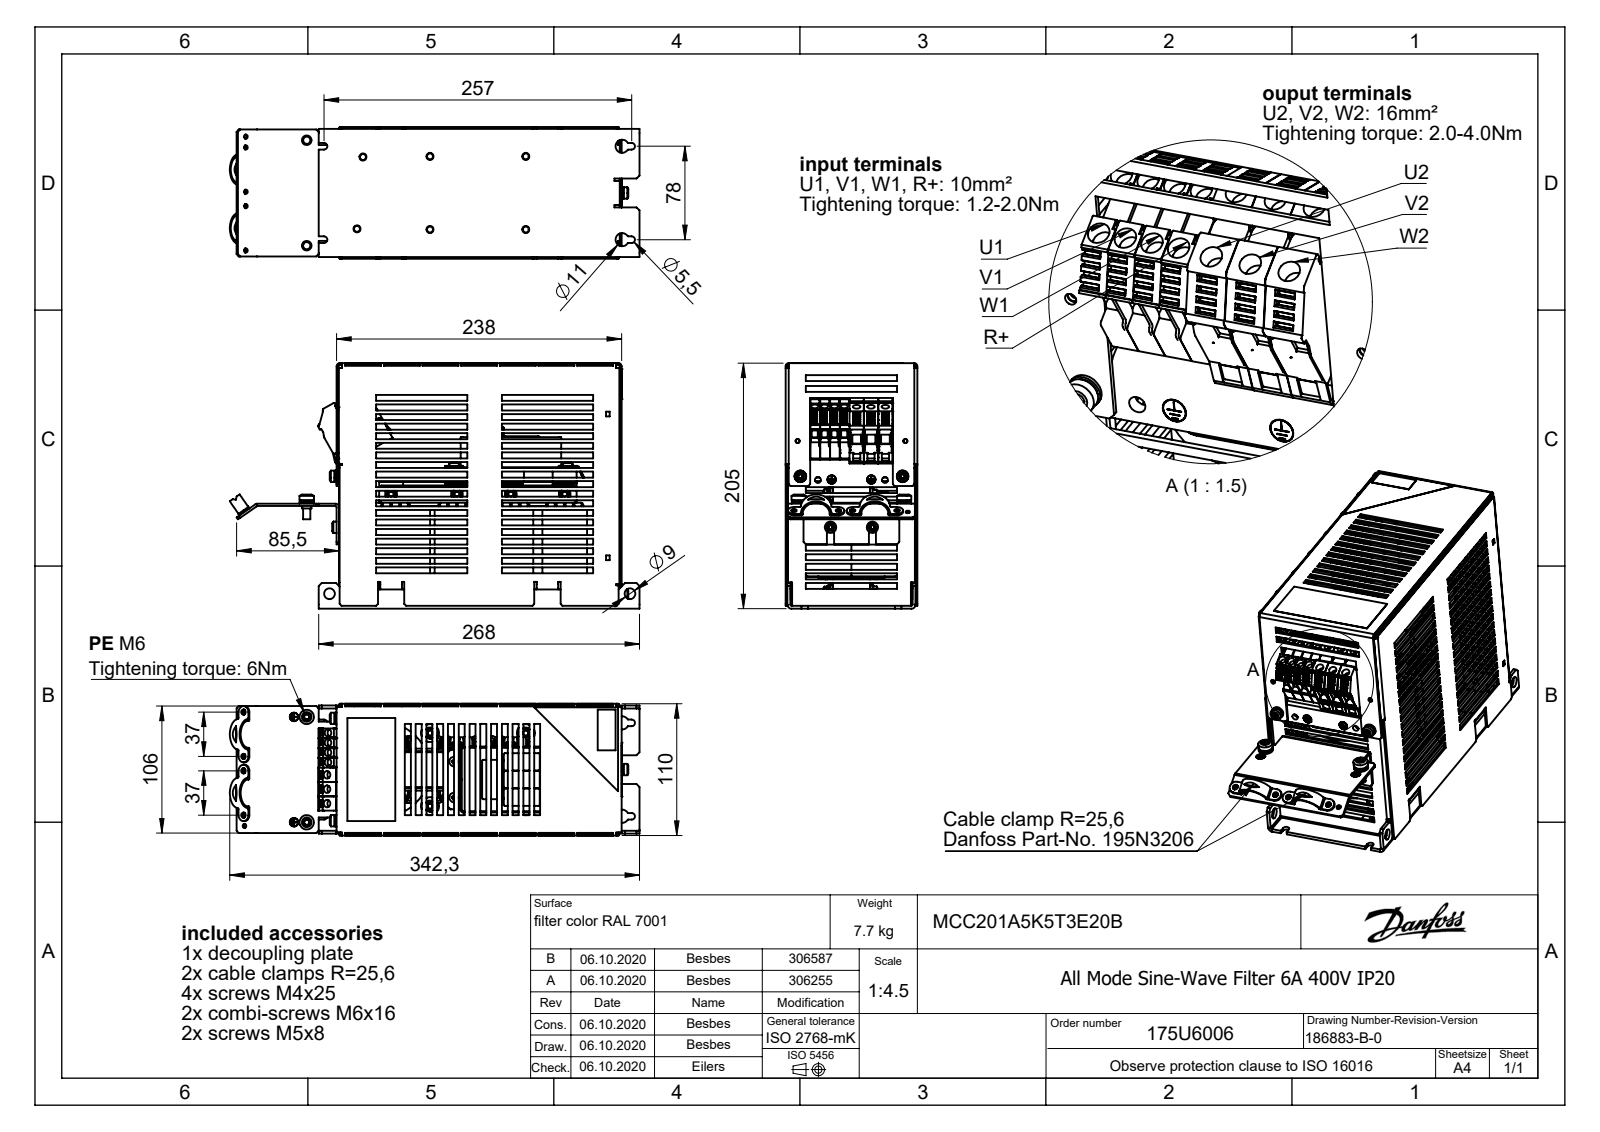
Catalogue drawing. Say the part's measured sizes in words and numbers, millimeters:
The part is named "129154; 128554; 141407; Tx-Schraube M4x50 ISO 14583 4.8 vz_Tx-Schraube M4x50 ISO 14583 4.8 vz (+8 more)". Its 3-D file was written by "SolidWorks 2018 (AUTOMOTIVE_DESIGN)". It is 110 solids with 9159 faces: 5623 planar, 2372 cylindrical and 1164 other. Overall it measures 342.27 by 205.2 by 110 millimeters. Its volume is 1 037 000 cubic millimeters and its surface area 884 526 square millimeters. Round holes: 21 of diameter 4.2, 19 of diameter 4.5, 16 of diameter 3, 16 of diameter 5, 14 of diameter 6.3, 12 of diameter 3.3, 12 of diameter 5.3, 8 of diameter 3.95, 8 of diameter 4.3, 6 of diameter 3.2, 6 of diameter 3.5, 5 of diameter 3.7. Round bosses or shafts: 16 of diameter 8, 11 of diameter 10, 8 of diameter 9, 7 of diameter 4, 6 of diameter 5.95, 6 of diameter 0.8, 5 of diameter 9.5, 5 of diameter 5. Partial cylindrical surfaces (rounded edges, fillets, slot ends): 291 of radius 0.3, 89 of radius 1, 76 of radius 0.15, 72 of radius 2, 64 of radius 0.19, 32 of radius 0.25, 32 of radius 0.41, 28 of radius 0.2. The main face-to-face distances are 1.5, 108.5, 2, 2.5, 39, 1, 107, 45, 70.5, 110. The hole center spacings are 45, 90, 32, 48.8, 58.36, 66.38, 100, 8.2.
